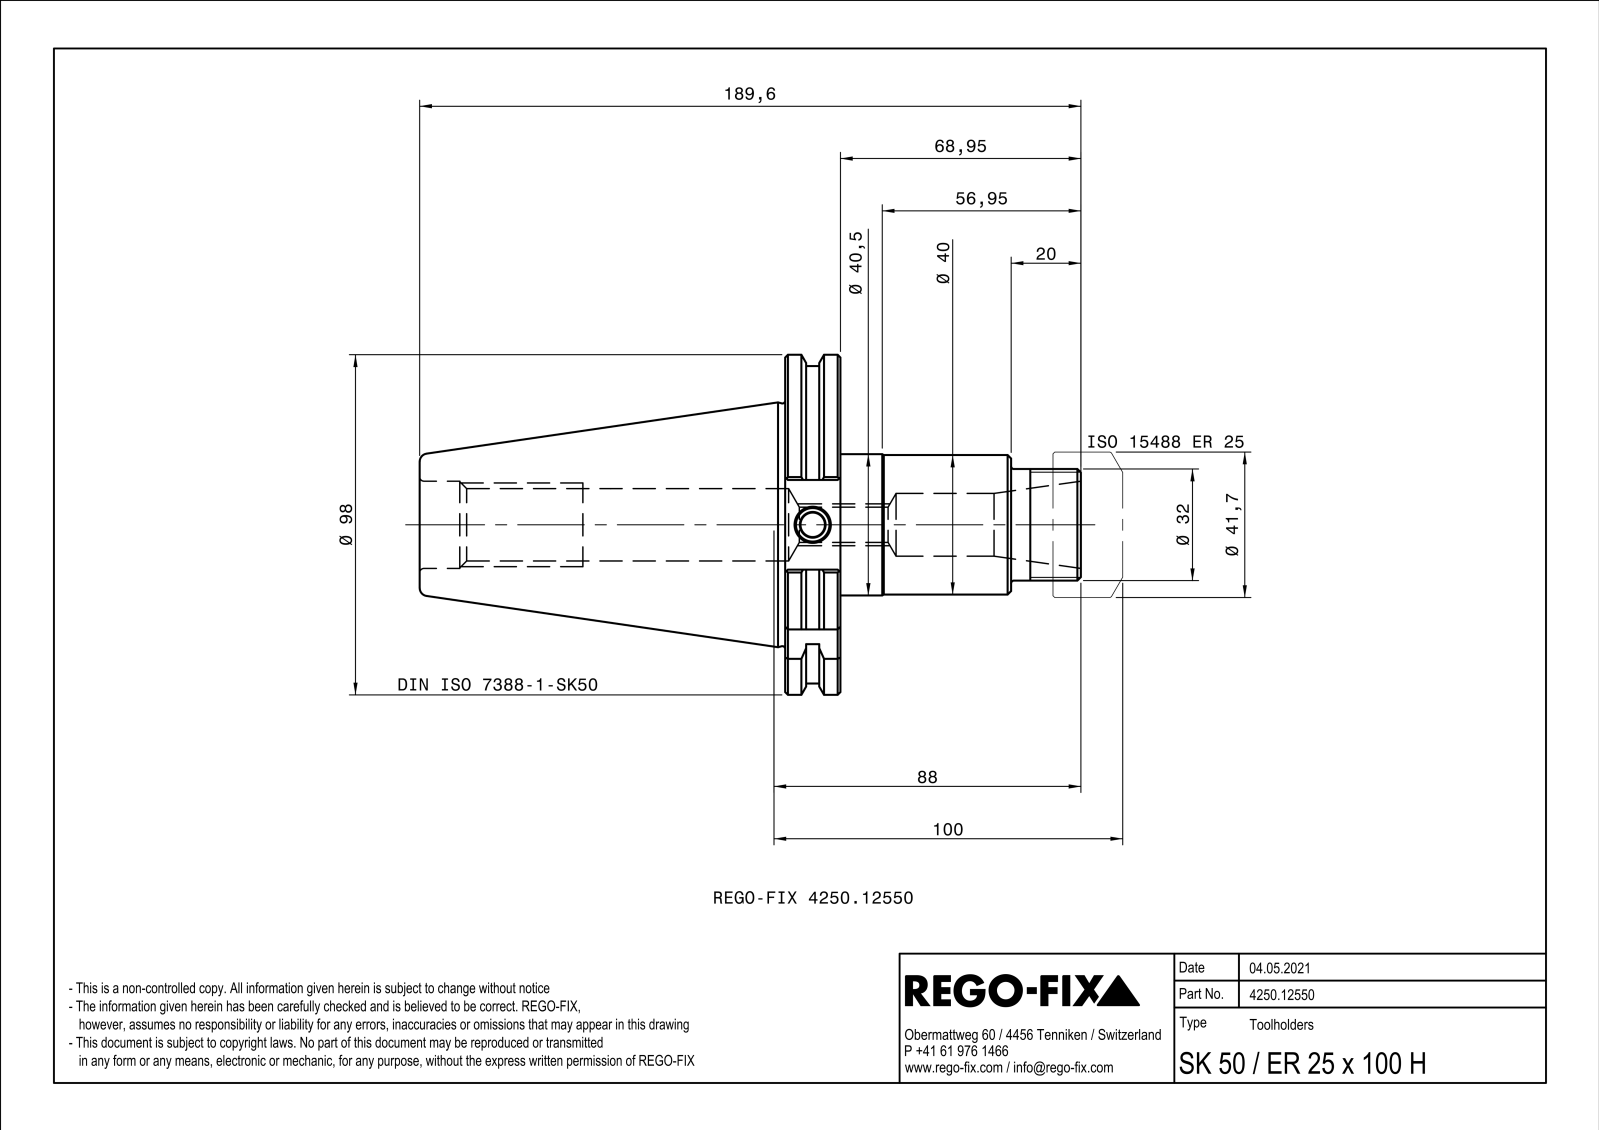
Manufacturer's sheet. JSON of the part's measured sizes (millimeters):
{"part_name": "NOCUT", "step_written_by": "SIEMENS PLM Software Solid Edge ST10 (AUTOMOTIVE_DESIGN)", "units": "millimeters", "bodies": {"solids": 1, "faces": 130, "planar": 42, "cylindrical": 37, "other": 51}, "overall_size": [189.6, 97.5, 93.58], "volume_mm3": 383692, "surface_area_mm2": 54979, "round_holes": [[3.5, 5], [7, 1], [10, 1], [10.11, 1], [18, 1], [20.75, 1], [25, 1]], "round_bosses_or_shafts": [[40.5, 1], [40, 1], [32, 1]], "partial_cylinders_radius": [[0.5, 5], [45.5, 1], [48.75, 1]], "face_to_face_distances": [15.85, 120.65, 104.8, 72.8, 48.95, 64.8, 169.6, 25.7, 20, 68.95]}
